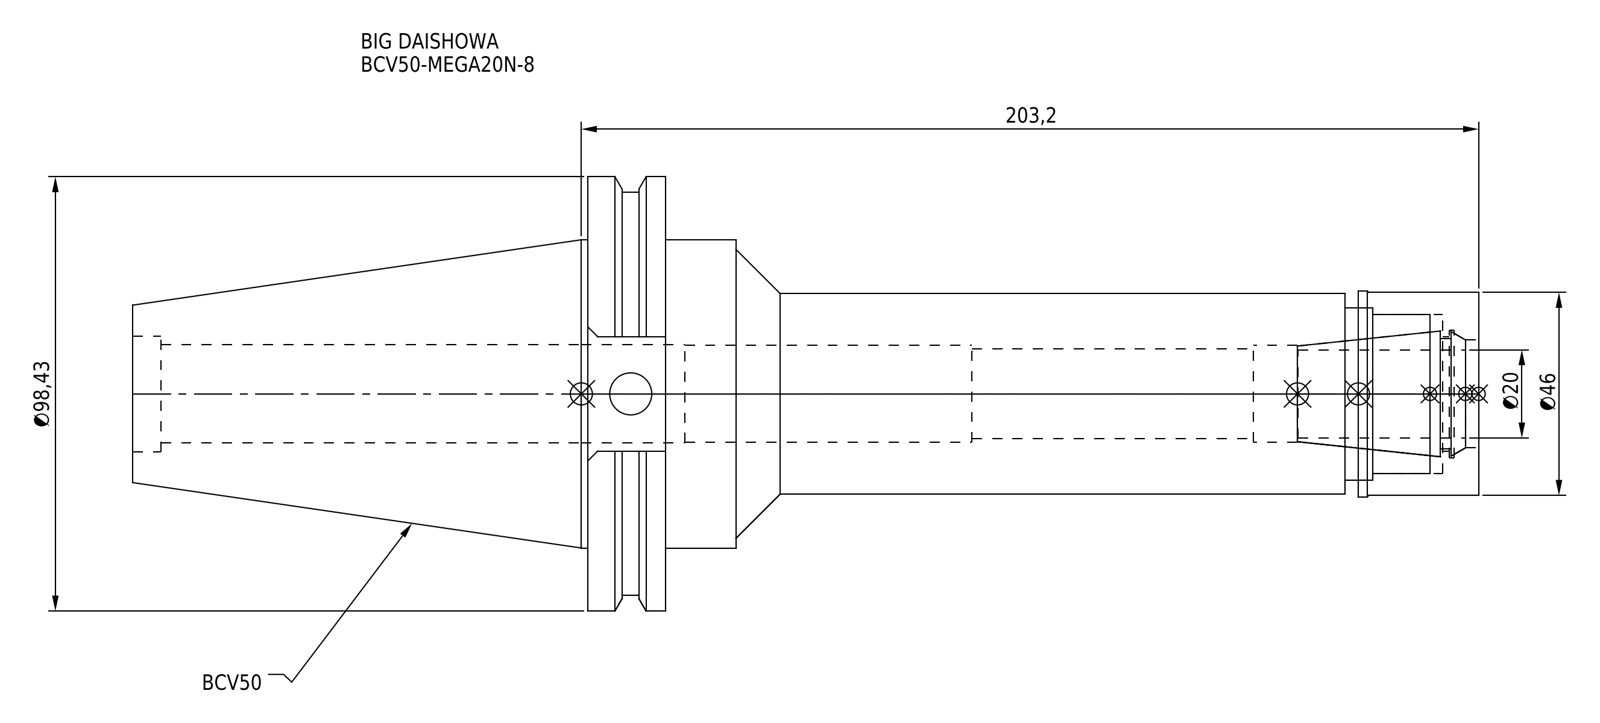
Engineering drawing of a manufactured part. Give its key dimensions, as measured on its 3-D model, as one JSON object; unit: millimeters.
{"part_name": "BCV50-MEGA20N-8_1.stp; BCV50-MEGA20N-8; BCV50MN20080-200_ASM.stp; BCV50-MEGA20N-8-200-FreeParts (+3 more)", "step_written_by": "SolidWorks 2019 (CONFIG_CONTROL_DESIGN)", "units": "millimeters", "bodies": {"solids": 2, "faces": 91, "planar": 33, "cylindrical": 44, "other": 14}, "overall_size": [304.8, 98.42, 94.95], "volume_mm3": 592978, "surface_area_mm2": 90321, "round_holes": [[9.53, 1], [20.3, 1], [22, 1], [22.3, 1], [24.5, 1], [26, 1], [26.23, 1], [29, 1], [36, 1], [39, 1]], "round_bosses_or_shafts": [[98.42, 1], [91.29, 1], [69.85, 1], [46.7, 1], [46, 1], [45.5, 1]], "face_to_face_distances": [17.55, 184.15, 201.7, 304.8, 120.65, 103.1, 27.2, 156.95, 174.5, 277.6]}
